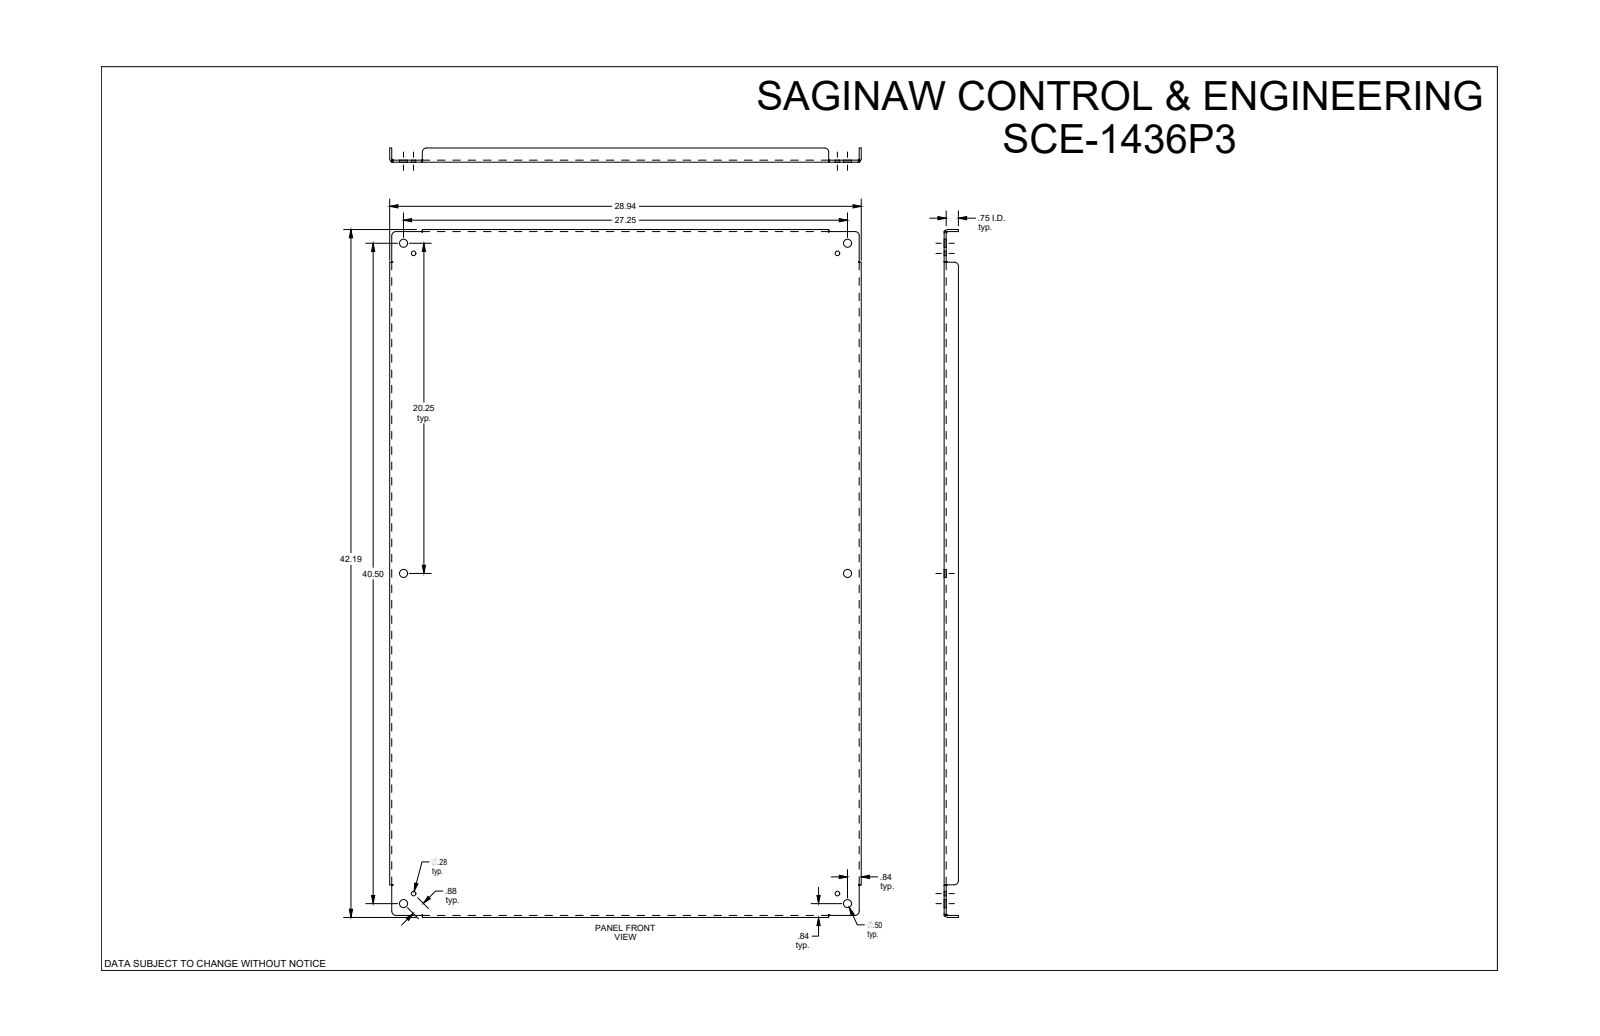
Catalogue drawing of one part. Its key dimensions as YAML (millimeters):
part_name: "SCE-1436P3"
step_written_by: "SolidWorks 2019 (CONFIG_CONTROL_DESIGN)"
units: millimeters
bodies: {solids: 1, faces: 84, planar: 30, cylindrical: 30, other: 24}
overall_size: [1071.6, 735, 22.2]
volume: 2668000
surface_area: 1694000
round_holes:
  - {diameter: 12.7, count: 6}
  - {diameter: 7.1, count: 4}
partial_cylinders:
  - {radius: 6.4, count: 8}
  - {radius: 2.8, count: 4}
  - {radius: 6, count: 4}
face_to_face_distances: [3.2, 3.2, 731.9, 1068.4, 728.6, 735, 1065.2, 1071.5, 19.1, 22.2]
hole_center_spacings: [22.2, 498.9, 514.4, 676.6, 840.4, 862.3, 1013.1, 1218.1]
